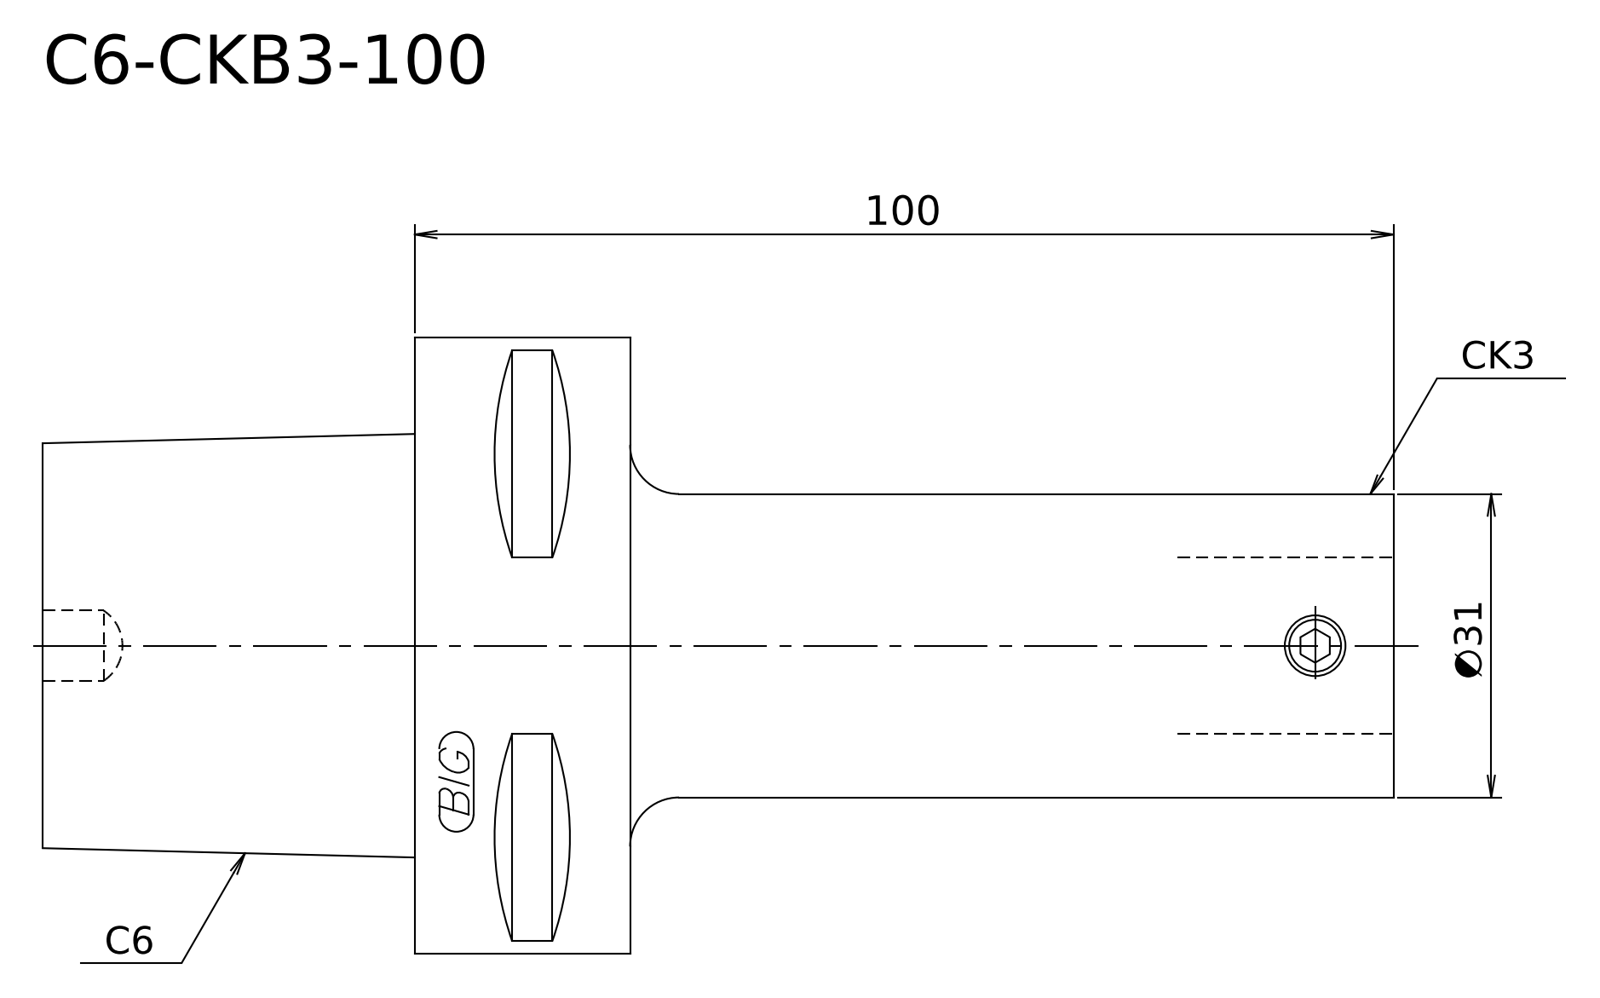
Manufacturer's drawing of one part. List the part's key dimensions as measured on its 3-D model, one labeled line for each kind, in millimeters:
STEP written by: Kubotek KeyCreator V8.5.1 (14335) (CONFIG_CONTROL_DESIGN)
Units: millimetres
Bodies: 1 solid, 10 faces (4 planar, 2 cylindrical, 4 other)
Overall size (bounding box): 138 × 62.98 × 62.98
Volume: 183 541 mm³ · Surface area: 22 958 mm²
Round bosses / shafts (diameter × count): ⌀62.98 ×1, ⌀31 ×1
Main face-to-face distances: 22, 60, 38, 78, 100, 138
